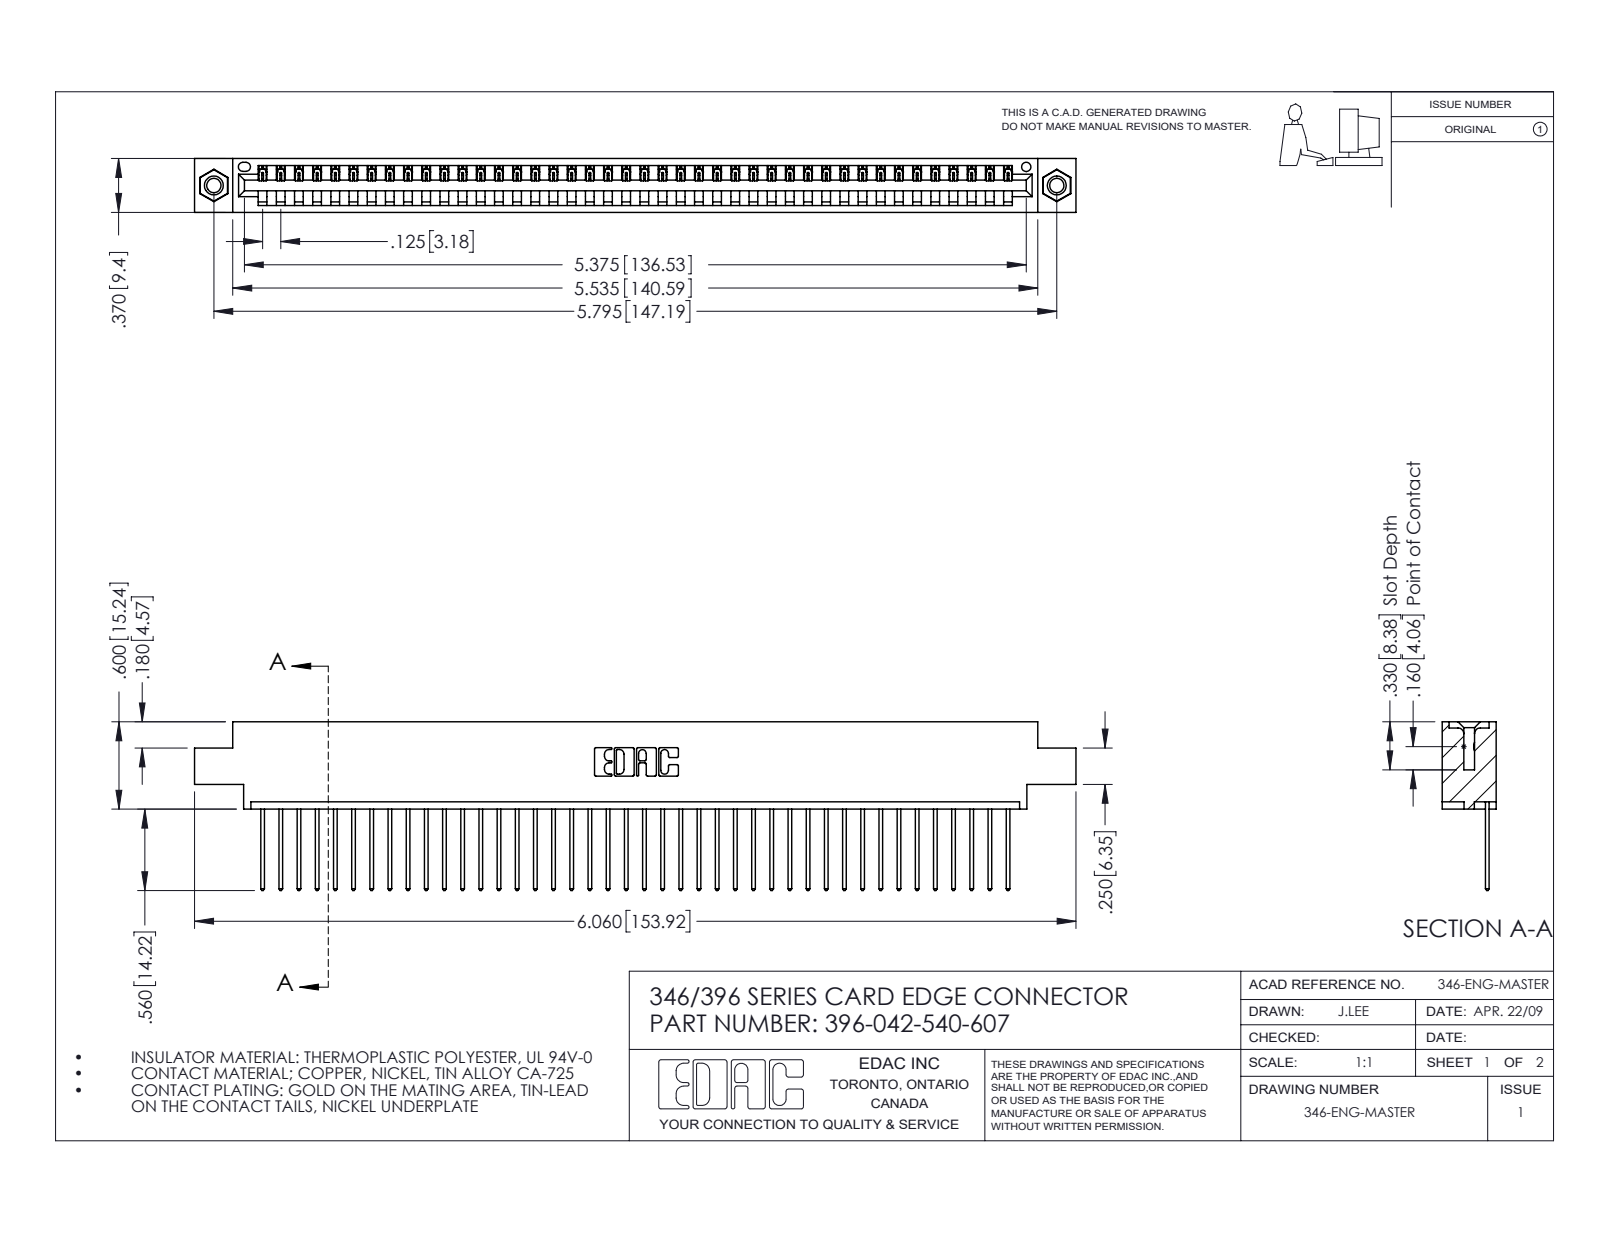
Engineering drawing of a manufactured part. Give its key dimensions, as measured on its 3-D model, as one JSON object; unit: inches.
{"part_name": "396-042-540-607; 346 Part_0.170 Offset - 0.156 Dia-TI; 345-250-001_345-250-005-103; 345-292-001_345-293-140", "step_written_by": "SolidWorks 2016 (CONFIG_CONTROL_DESIGN)", "units": "inches", "bodies": {"solids": 45, "faces": 2622, "planar": 1792, "cylindrical": 814, "other": 16}, "overall_size": [6.06, 1.16, 0.37], "volume_in3": 0.892, "surface_area_in2": 29.27, "round_holes": [[0.098, 2], [0.125, 2], [0.156, 2], [0.064, 1]], "round_bosses_or_shafts": [[0.155, 2]], "partial_cylinders_radius": [[0.006, 84], [0.01, 84], [0.01, 22], [0.007, 6], [0.031, 6], [0.026, 3], [0.031, 2], [0.04, 2]], "face_to_face_distances": [0.048, 0.322, 0.37, 0.25, 0.072, 0.298, 0.025, 0.222, 0.148, 0.1], "hole_center_spacings": [0.246, 5.586, 5.795]}
